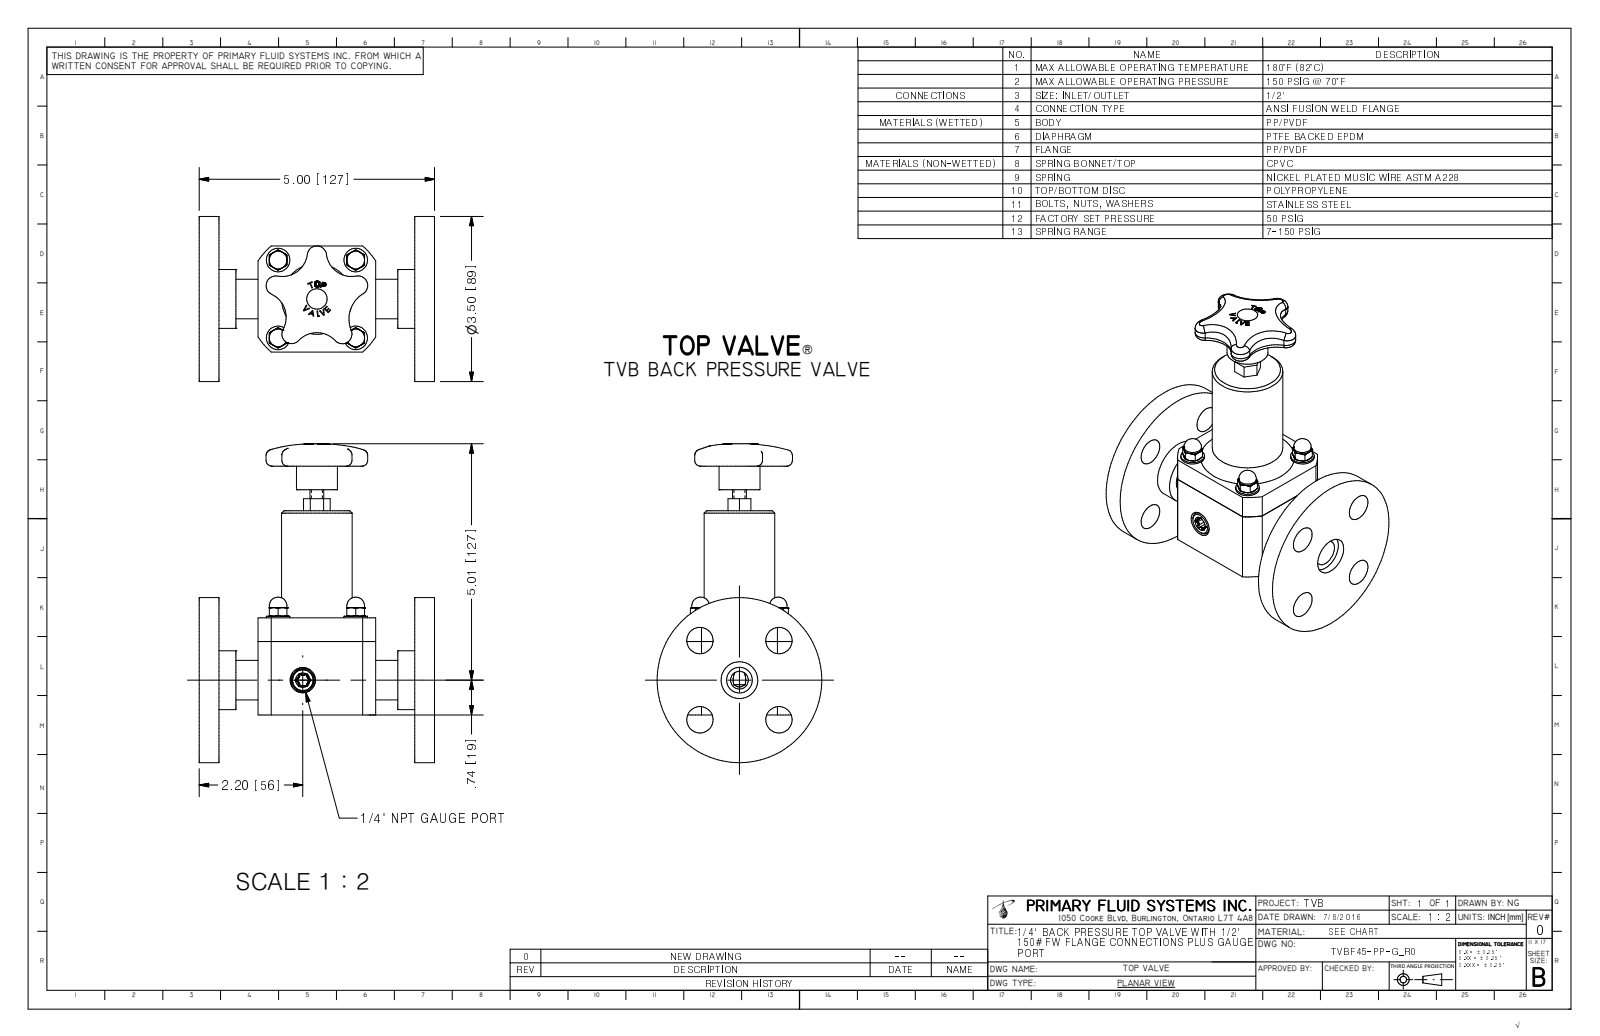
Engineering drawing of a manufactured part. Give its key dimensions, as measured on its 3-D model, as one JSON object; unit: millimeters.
{"part_name": "TVBF45-PP-G_R0", "step_written_by": "Autodesk Inventor 2009 (AUTOMOTIVE_DESIGN)", "units": "millimeters", "bodies": {"solids": 1, "faces": 383, "planar": 156, "cylindrical": 67, "other": 160}, "overall_size": [171.8, 127, 88.9], "volume_mm3": 399200, "surface_area_mm2": 73290, "round_holes": [[3.7, 4], [14.2, 4], [13.9, 1], [19.8, 1]], "round_bosses_or_shafts": [[12.7, 4], [9.5, 4], [7.9, 4], [88.9, 1], [38.1, 1], [31.8, 1], [22.1, 1], [21.3, 1]], "partial_cylinders_radius": [[0.7, 6], [2.2, 5], [5.2, 5], [13.6, 4], [16.7, 4], [15.9, 1], [18.9, 1], [37.8, 1]], "face_to_face_distances": [10.7, 116.3, 127, 105.7, 31.8, 95.3, 21.1, 84.6, 57.2, 63.5], "hole_center_spacings": [41.9, 30.1, 30.2, 42.6, 42.7, 59.3, 60.3]}
